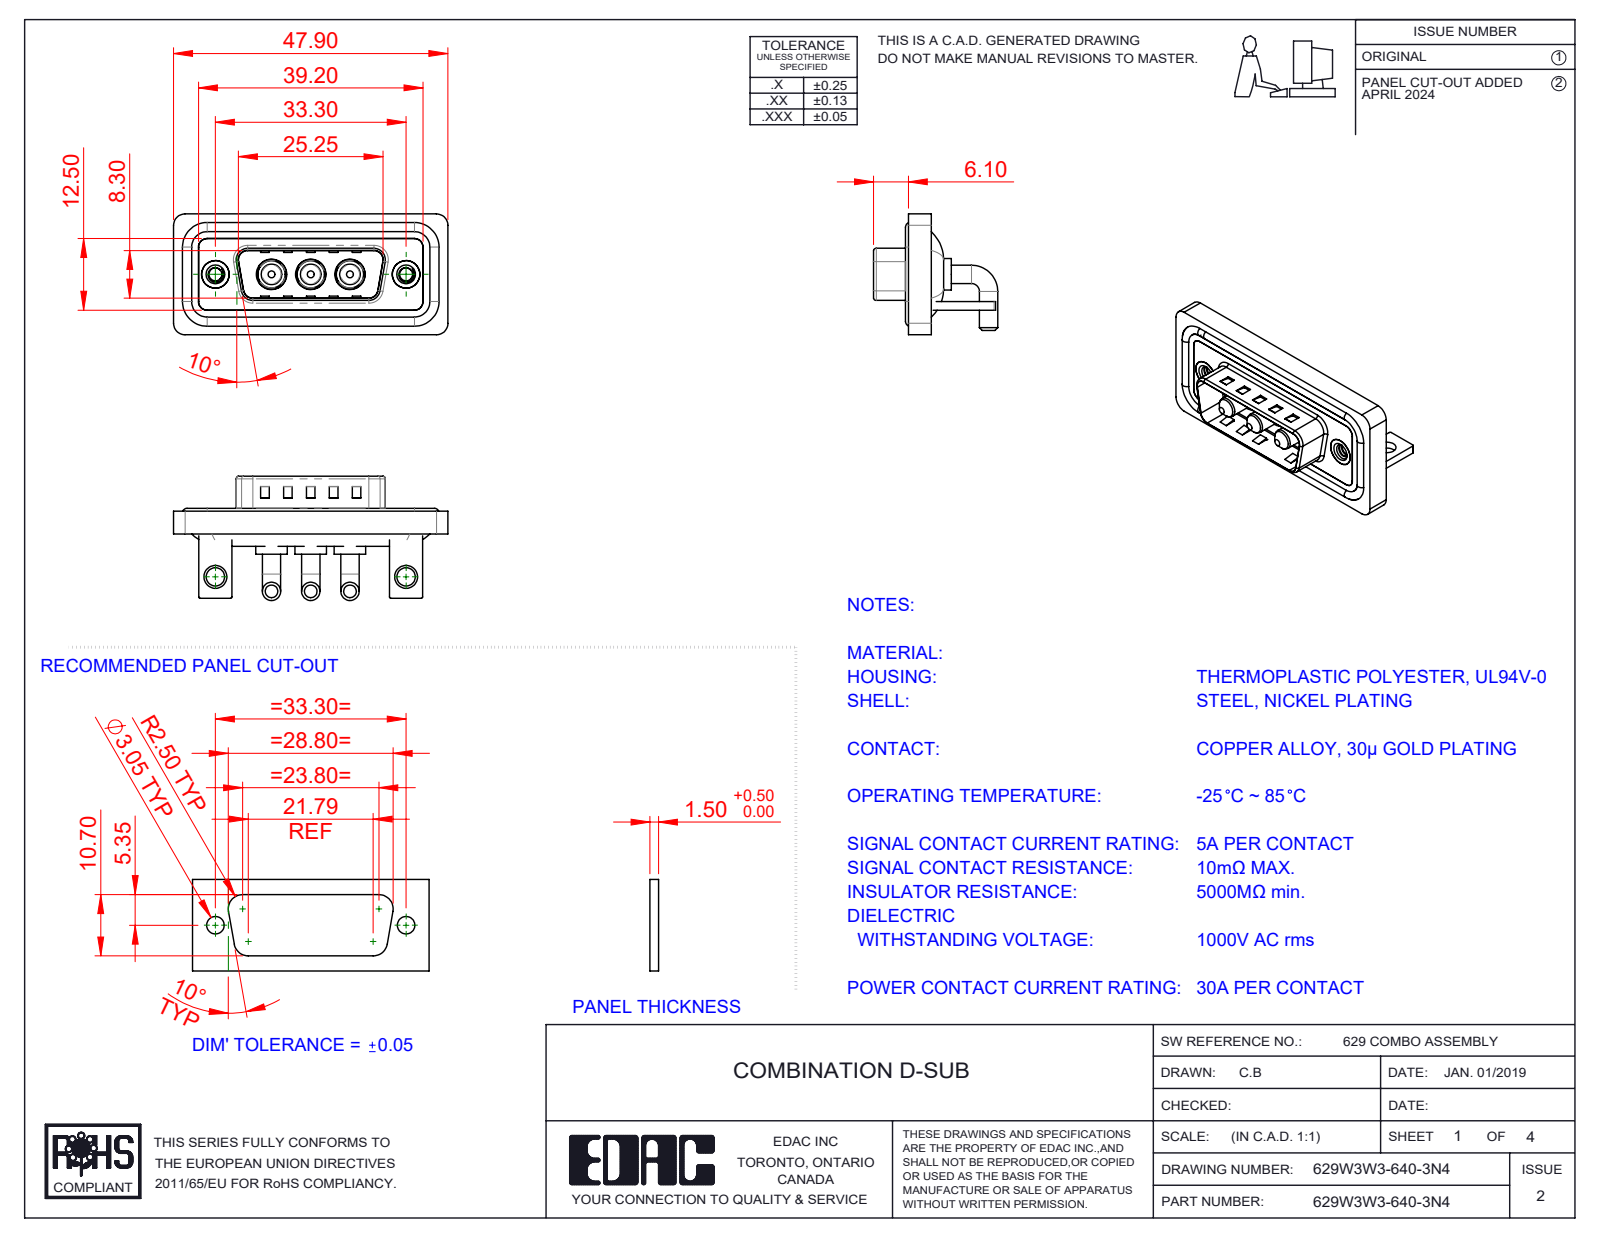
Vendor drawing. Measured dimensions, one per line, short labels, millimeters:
name: 629Combo Stabilizer Bracket; 629Combo Housing_3W3; 629Combo Threaded Rivet_3; Power Pin_30A RA (+4 more)
written by: SolidWorks 2023 (CONFIG_CONTROL_DESIGN)
unit: mm
bodies: 15 solids, 616 faces (227 planar, 265 cylindrical, 124 other)
size: 47.9 × 21.7 × 21.1
volume: 6 140 mm³; area: 9 678 mm²
holes: 3× ⌀4.85, 3× ⌀5.3, 2× ⌀2.26, 2× ⌀3.2, 2× ⌀4, 2× ⌀4.8, 2× ⌀5
bosses: 6× ⌀3.2, 4× ⌀1.6, 3× ⌀5.5, 3× ⌀5.2, 3× ⌀4.75, 3× ⌀3.75, 3× ⌀3.6, 2× ⌀4.9
rounds: 21× R2, 18× R1.5, 16× R0.25, 9× R0.5, 8× R1.6, 4× R0.6, 4× R0.65, 4× R0.9
face distances: 0.4, 1.5, 0.8, 2.9, 1.1, 2.1, 3.7, 1.6, 1.2, 4.5
hole spacings: 6.85, 9.8, 16.65, 23.5, 33.3, 13.7
